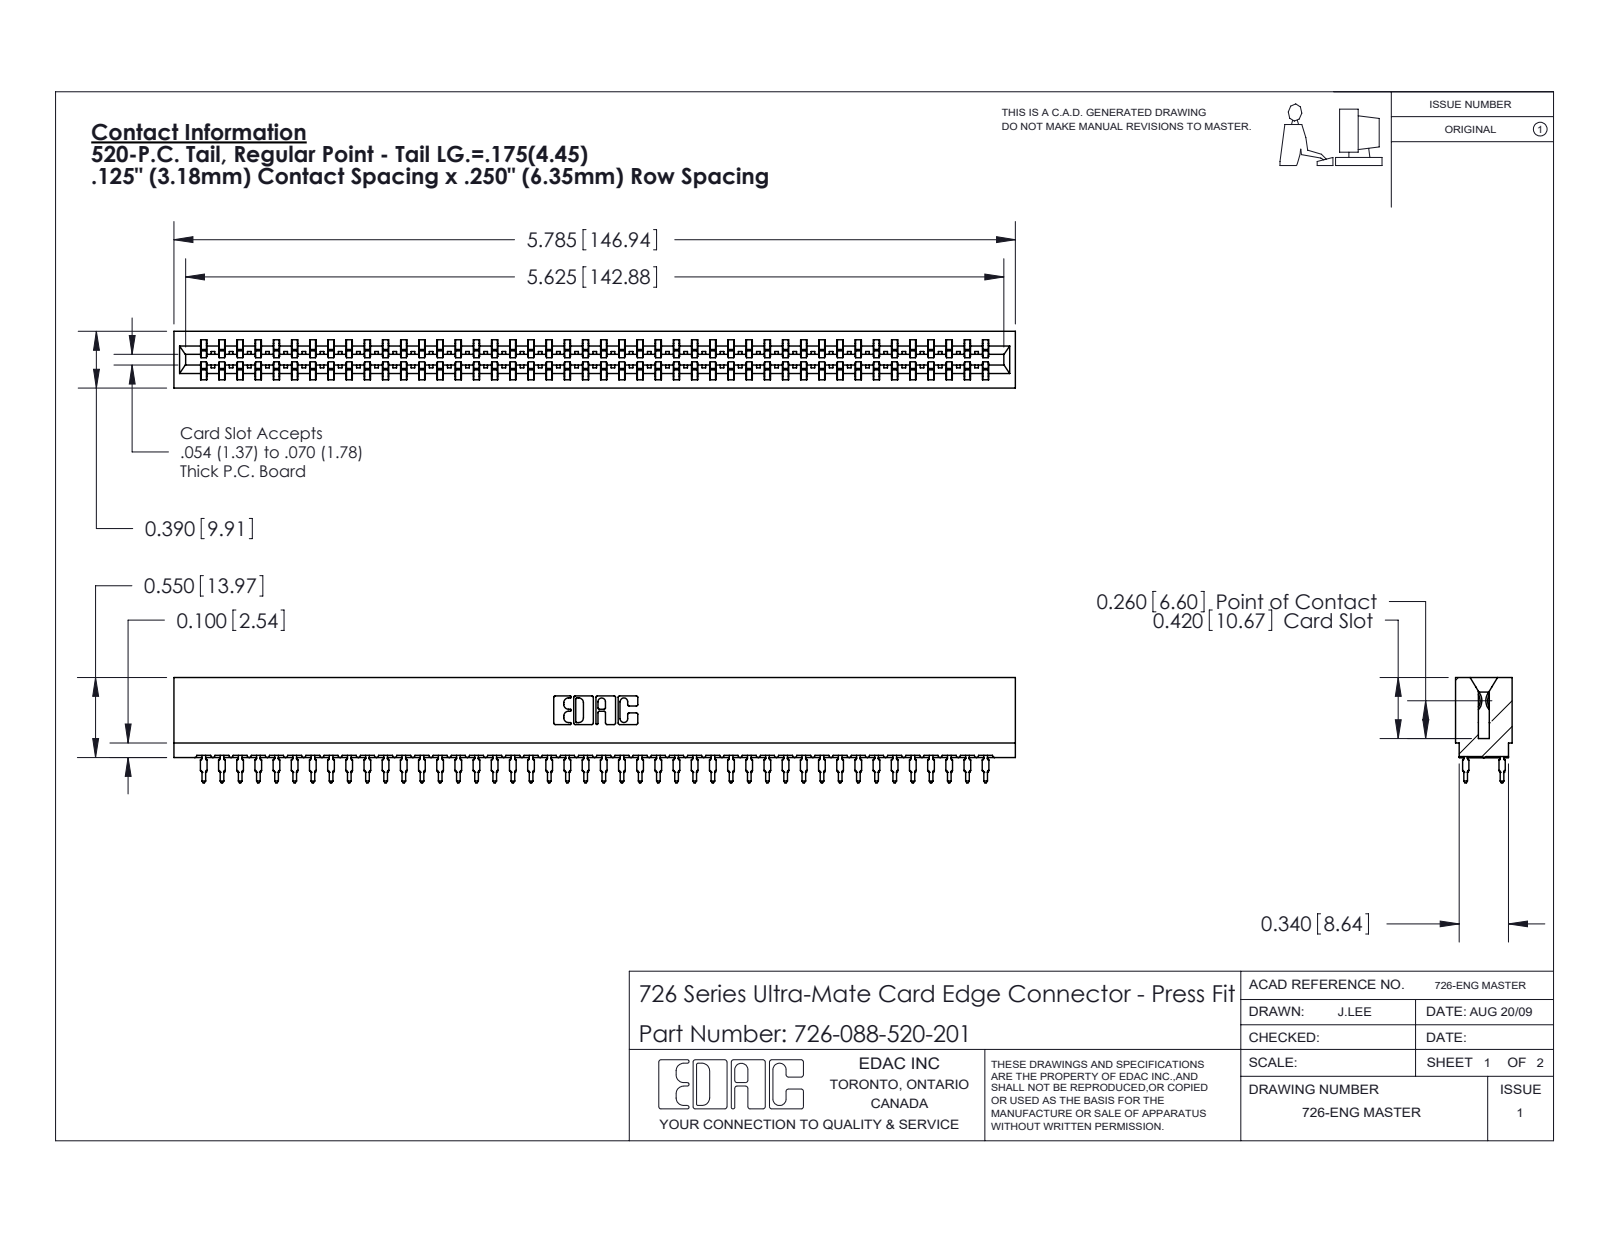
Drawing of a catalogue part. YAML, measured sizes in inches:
part_name: "726 Part_.515 Slot Depth - 01; 746-292-001_520; 726-088-520-201"
step_written_by: "SolidWorks 2020 (CONFIG_CONTROL_DESIGN)"
units: inches
bodies: {solids: 89, faces: 7973, planar: 4103, cylindrical: 1582, other: 2288}
overall_size: [5.785, 0.724, 0.39]
volume: 0.82
surface_area: 34.17
partial_cylinders:
  - {radius: 0.021, count: 176}
  - {radius: 0.015, count: 45}
  - {radius: 0.01, count: 22}
  - {radius: 0.005, count: 8}
  - {radius: 0.011, count: 8}
  - {radius: 0.007, count: 6}
  - {radius: 0.031, count: 6}
  - {radius: 0.026, count: 3}
face_to_face_distances: [0.057, 0.333, 0.39, 0.025, 0.307, 0.25, 0.275, 0.083, 0.365, 0.032]
